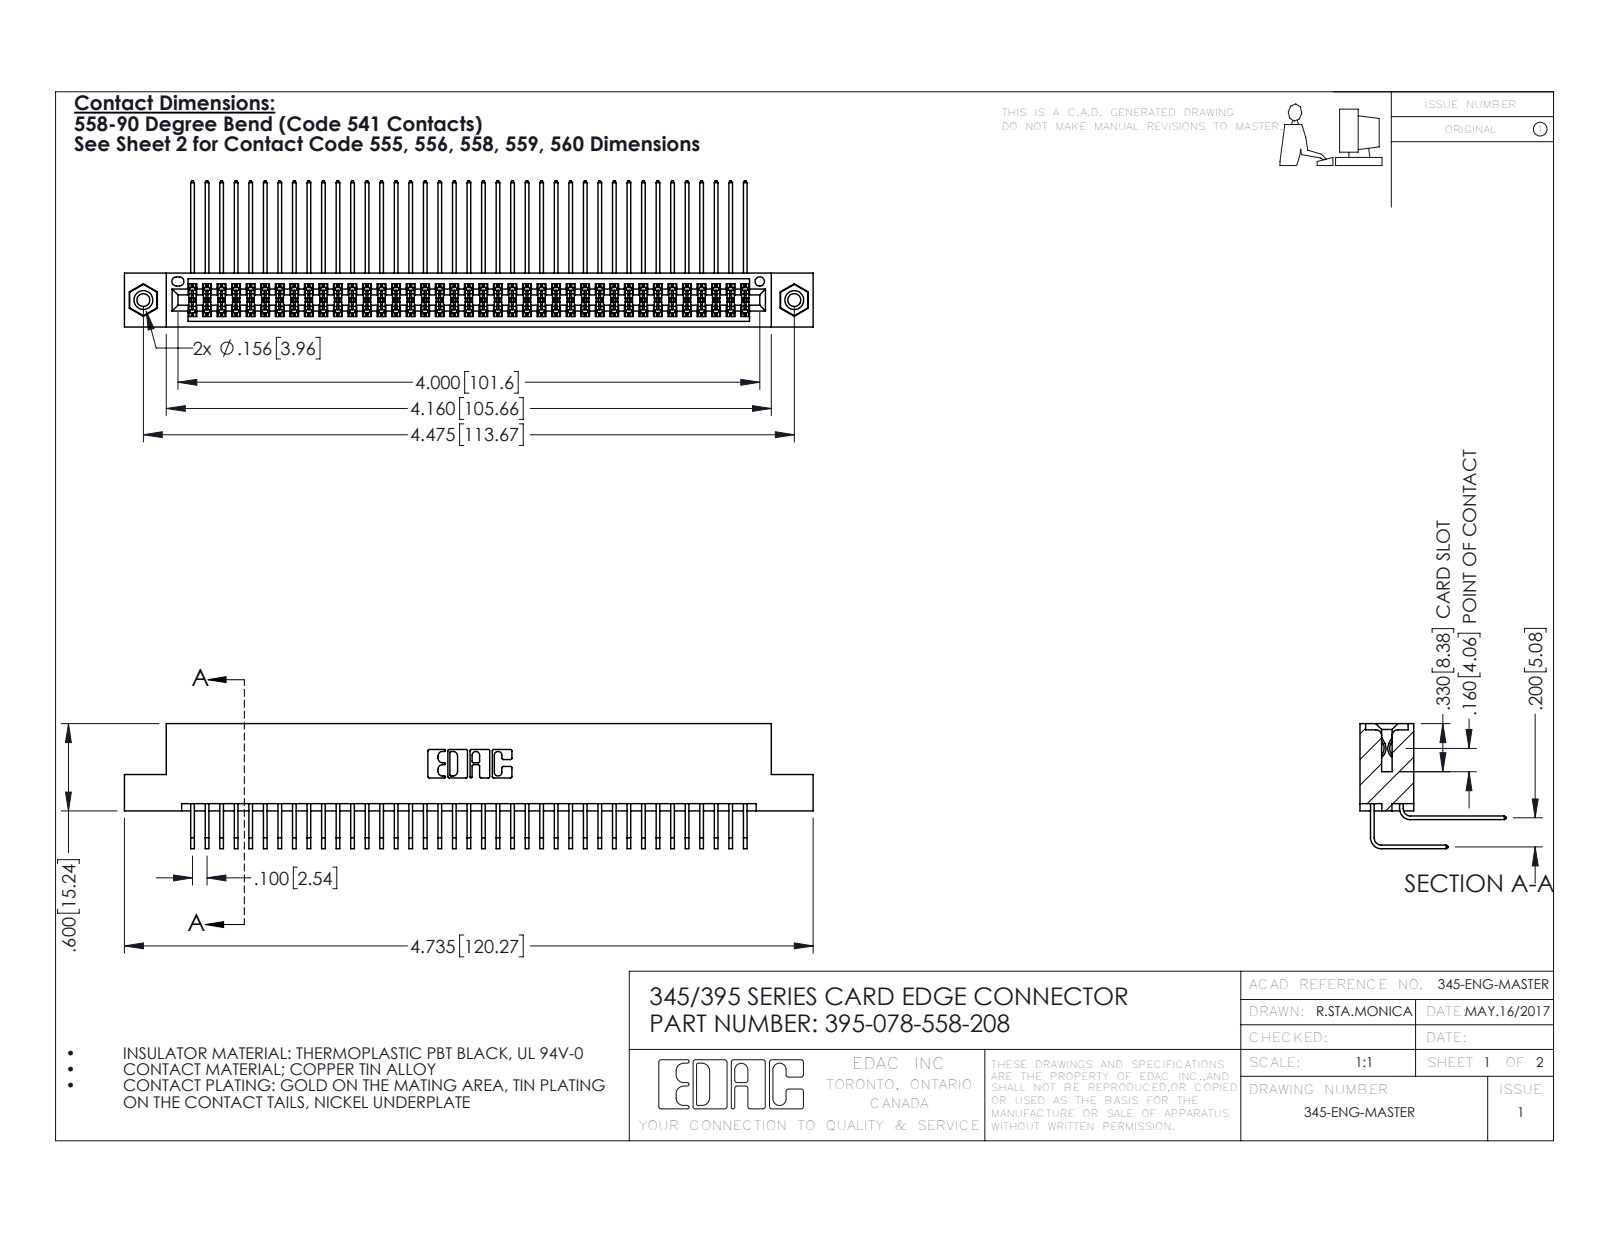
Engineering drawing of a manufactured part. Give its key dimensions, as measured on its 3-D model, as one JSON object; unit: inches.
{"part_name": "345 Part_Flush Mounting Lugs - 0.156 Dia-TI; 395-078-558-208; 345-292-001_558 559 Tail - 1; 345-250-001_345-250-003-102 (+1 more)", "step_written_by": "SolidWorks 2016 (CONFIG_CONTROL_DESIGN)", "units": "inches", "bodies": {"solids": 81, "faces": 4242, "planar": 2842, "cylindrical": 1384, "other": 16}, "overall_size": [4.735, 1.005, 0.859], "volume_in3": 0.738, "surface_area_in2": 30.93, "round_holes": [[0.089, 2], [0.125, 2], [0.156, 2], [0.064, 1]], "round_bosses_or_shafts": [[0.155, 2]], "partial_cylinders_radius": [[0.006, 118], [0.01, 22], [0.007, 6], [0.031, 6], [0.026, 3], [0.014, 2], [0.019, 2], [0.022, 2]], "face_to_face_distances": [0.072, 0.298, 0.2, 0.37, 0.098, 0.272, 0.025, 0.225, 0.025, 0.175], "hole_center_spacings": [0.27, 4.239, 4.475]}
